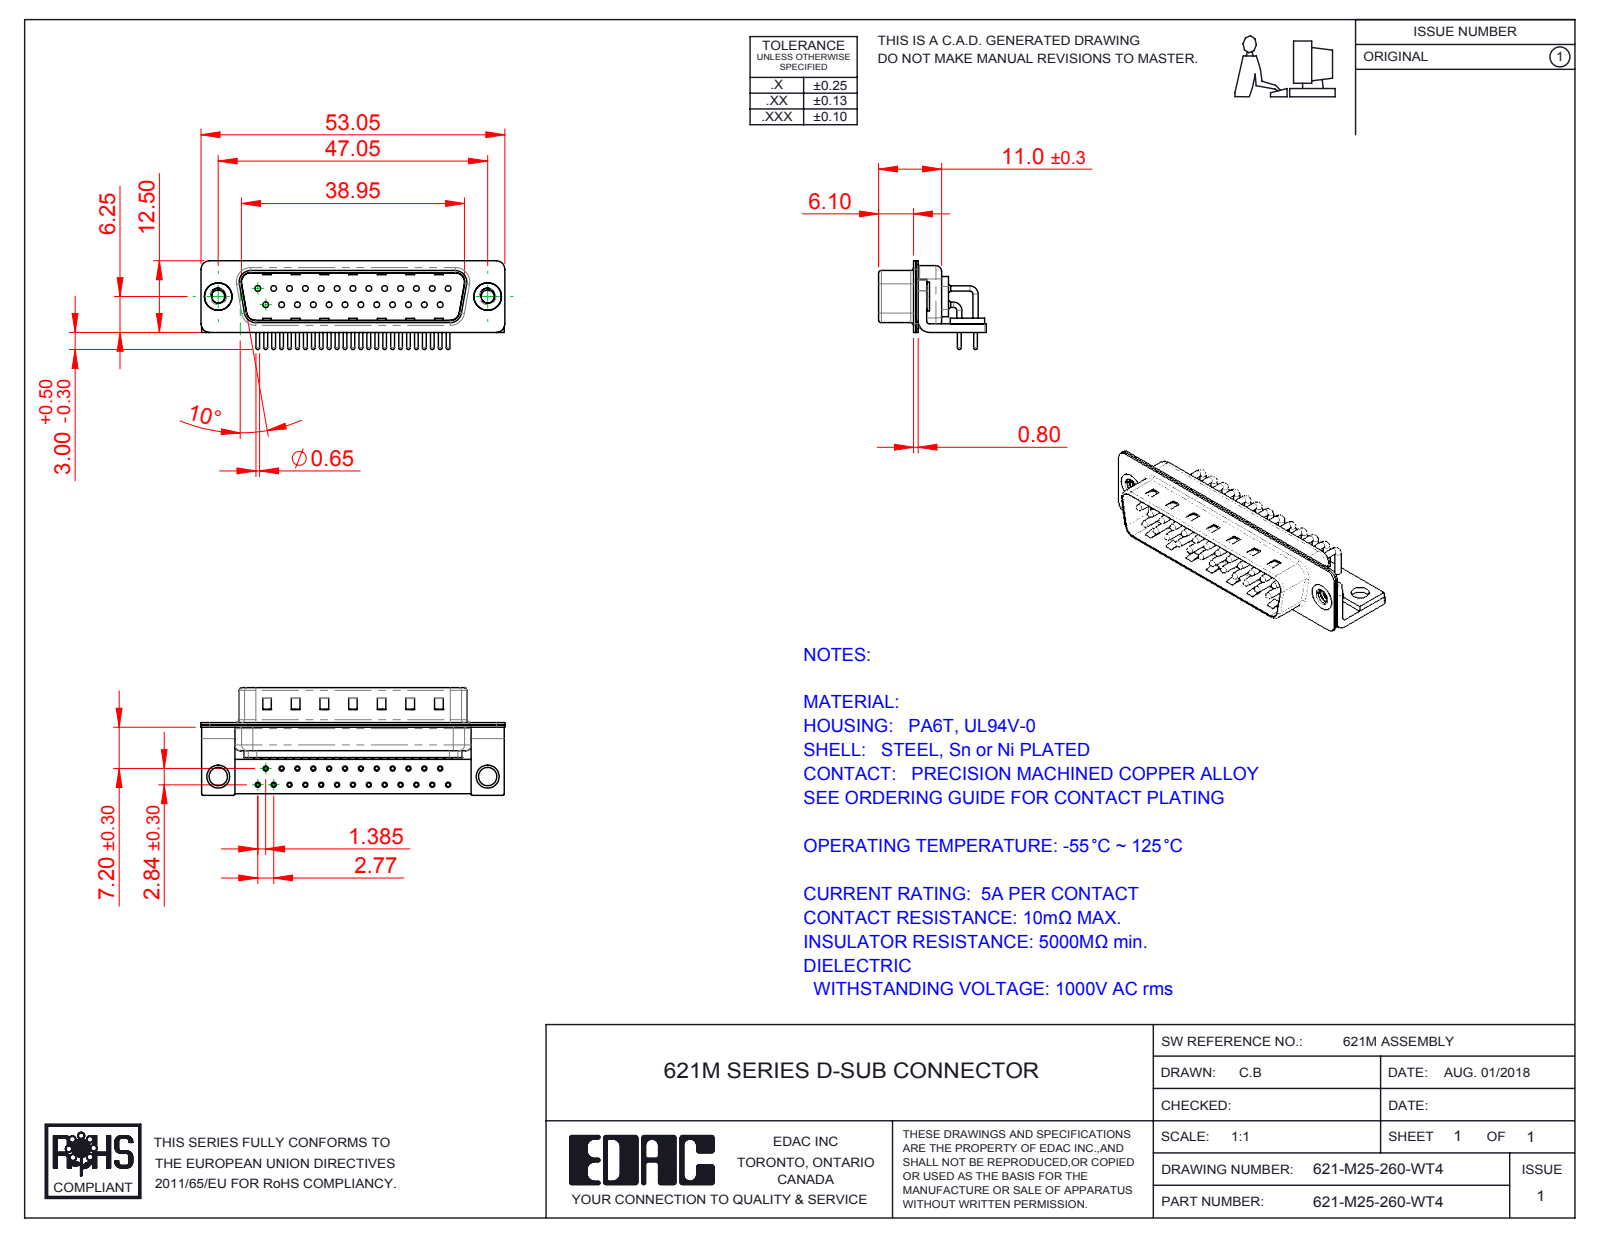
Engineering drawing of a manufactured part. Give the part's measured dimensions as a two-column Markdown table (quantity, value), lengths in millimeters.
| quantity | value |
| --- | --- |
| part name | 621M Shell Front_25 Contacts; 621M Housing_25 Contacts; 621M Shell Rear_25 Contacts; 621M Contact Row 2 (+5 more) |
| STEP written by | SolidWorks 2016 (CONFIG_CONTROL_DESIGN) |
| units | millimeters |
| bodies | 33 solids, 3226 faces (1797 planar, 1109 cylindrical, 320 other) |
| overall size | 53.05 × 18.8 × 15.49 |
| volume | 3 385 mm³ |
| surface area | 8 887 mm² |
| round holes (diameter × count) | 0.9 × 25, 1 × 25, 1.7 × 25, 2 × 25, 2.26 × 2, 3.2 × 2, 4 × 2, 4.8 × 2 |
| round bosses / shafts (diameter × count) | 0.9 × 33, 1.5 × 25, 0.65 × 25, 5 × 2, 4.9 × 2 |
| partial cylindrical surfaces (radius × count) | 1.01 × 25, 0.25 × 16, 1.5 × 16, 2 × 13, 0.5 × 9, 1.6 × 8, 0.6 × 4, 0.65 × 4 |
| main face-to-face distances | 0.4, 0.85, 1.25, 1.5, 9.55, 0.8, 10.4, 1, 8.3, 8.7 |
| hole center spacings | 3.16, 2.77, 8.31, 5.54, 11.08, 13.85, 5.04, 16.62 |
